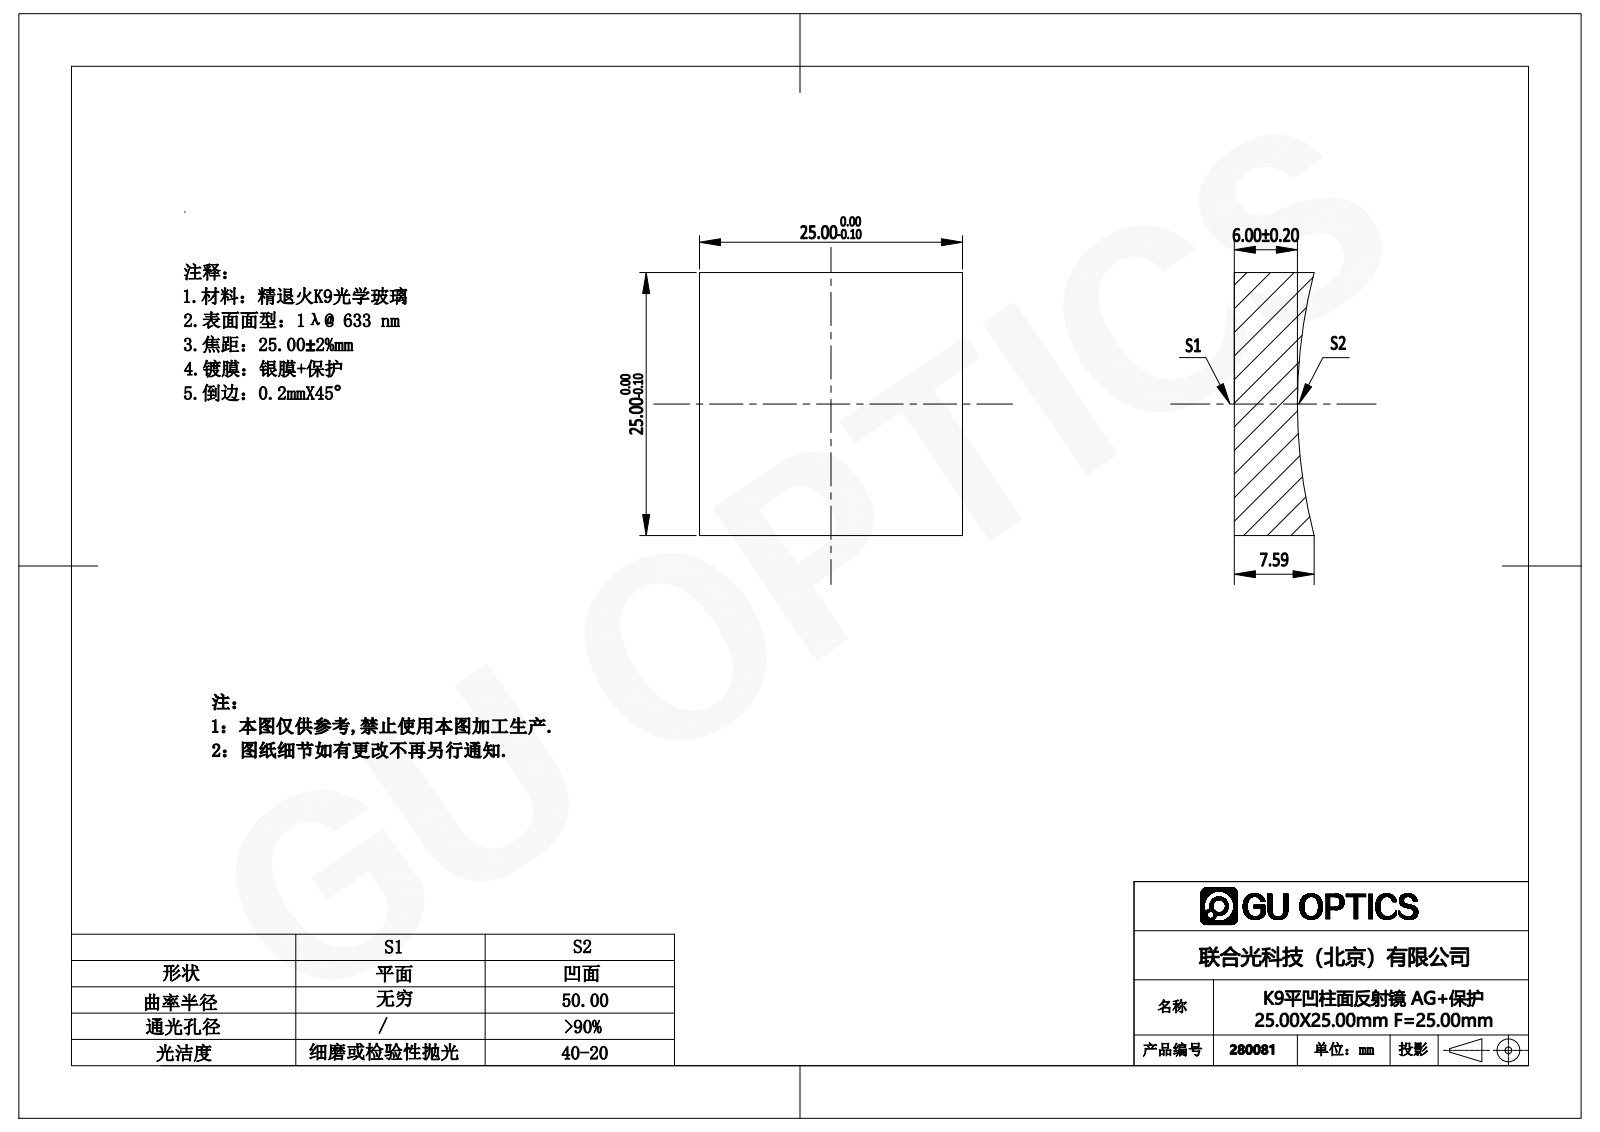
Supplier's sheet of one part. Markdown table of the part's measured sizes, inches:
| quantity | value |
| --- | --- |
| part name | 280015 |
| STEP written by | SolidWorks 2016 (AUTOMOTIVE_DESIGN) |
| units | inches |
| bodies | 1 solid, 7 faces (5 planar, 2 cylindrical, 0 other) |
| overall size | 0.984 × 0.984 × 0.299 |
| volume | 0.249 in³ |
| surface area | 3.041 in² |
| partial cylindrical surfaces (radius × count) | 1.969 × 1 |
| main face-to-face distances | 0.984 |
